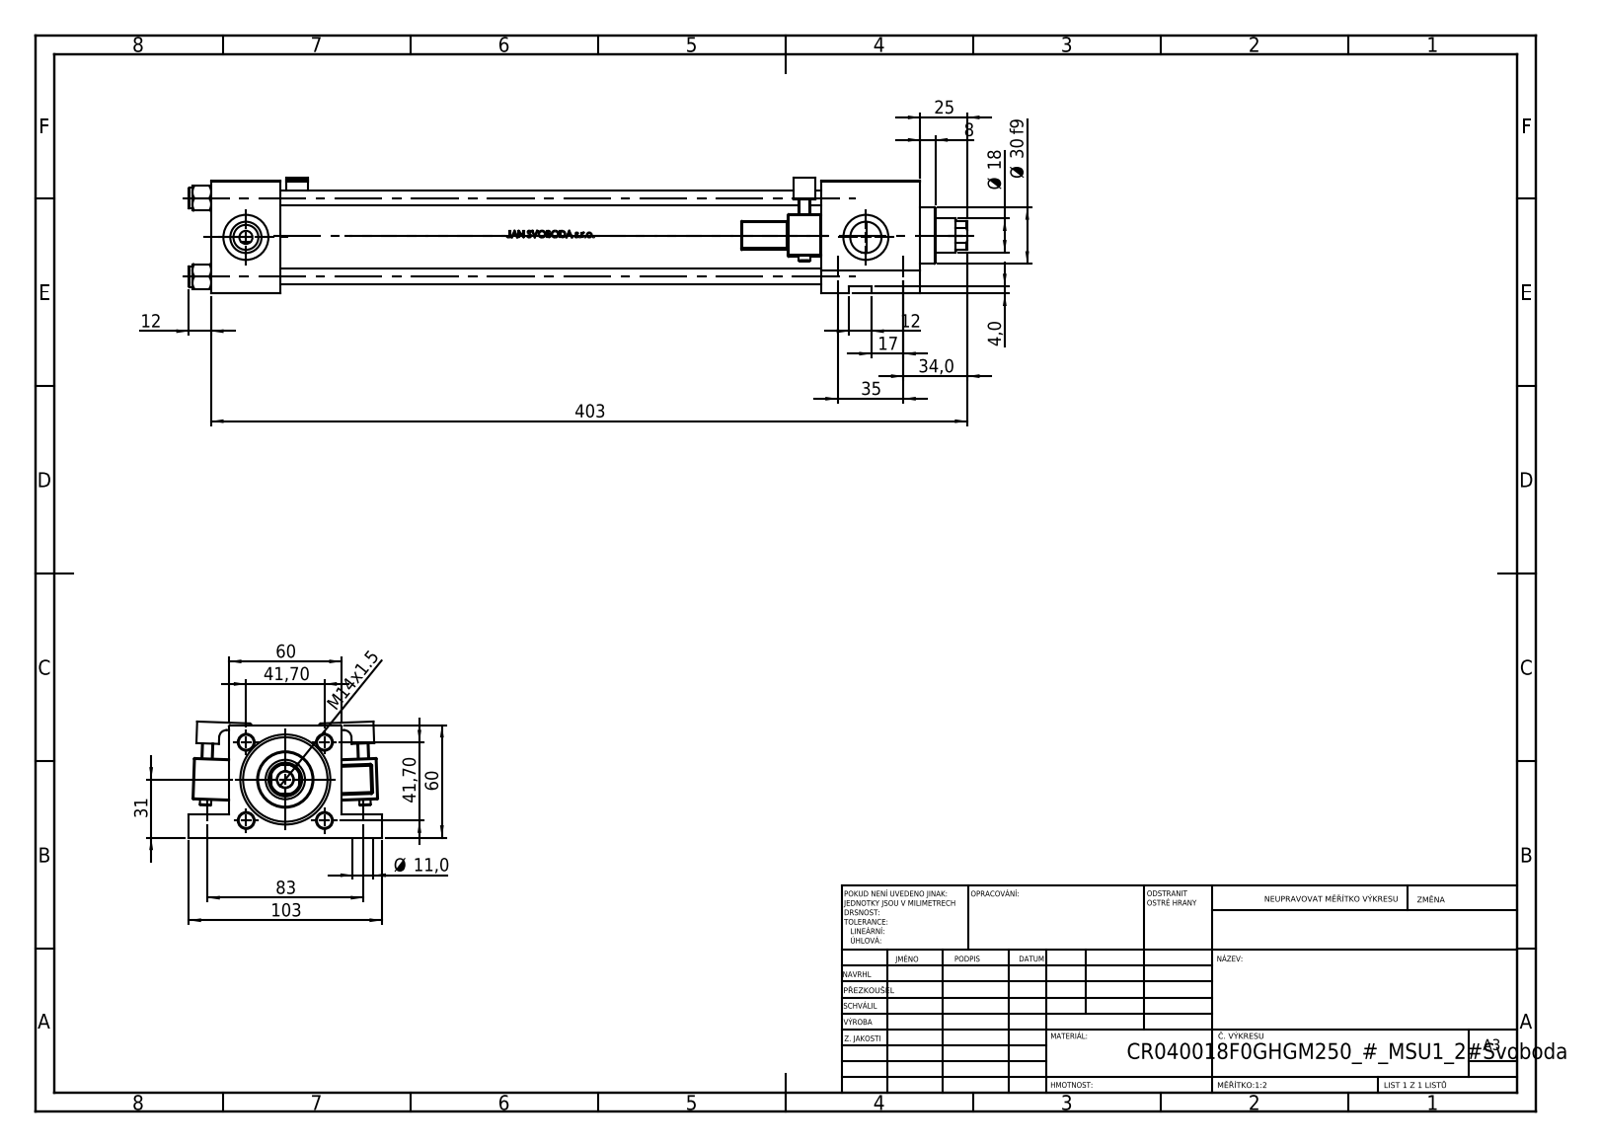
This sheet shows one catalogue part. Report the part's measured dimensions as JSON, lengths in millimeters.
{"part_name": "V215CR_F_TYCINKA; V215CR_F_Body; V215CR_VCP_F; V215CR_MSU (+2 more)", "step_written_by": "SolidWorks 2019 (CONFIG_CONTROL_DESIGN)", "units": "millimeters", "bodies": {"solids": 13, "faces": 1272, "planar": 495, "cylindrical": 201, "other": 576}, "overall_size": [415, 103, 61.9], "volume_mm3": 662451, "surface_area_mm2": 221893, "round_holes": [[8, 4], [11, 4], [7, 2], [16.66, 2], [24, 2], [8.5, 1], [18, 1], [21, 1], [31, 1], [40, 1], [45, 1]], "round_bosses_or_shafts": [[11, 4], [6, 2], [46, 1], [30, 1]], "partial_cylinders_radius": [[0.5, 48], [1, 2], [2.5, 2], [4, 2], [8.5, 1]], "face_to_face_distances": [60, 37, 325, 288, 378, 341, 53, 349.3, 312.3, 24.3], "hole_center_spacings": [41.7, 28.79, 30.2, 35, 58.97, 83, 90.08, 330.5]}
